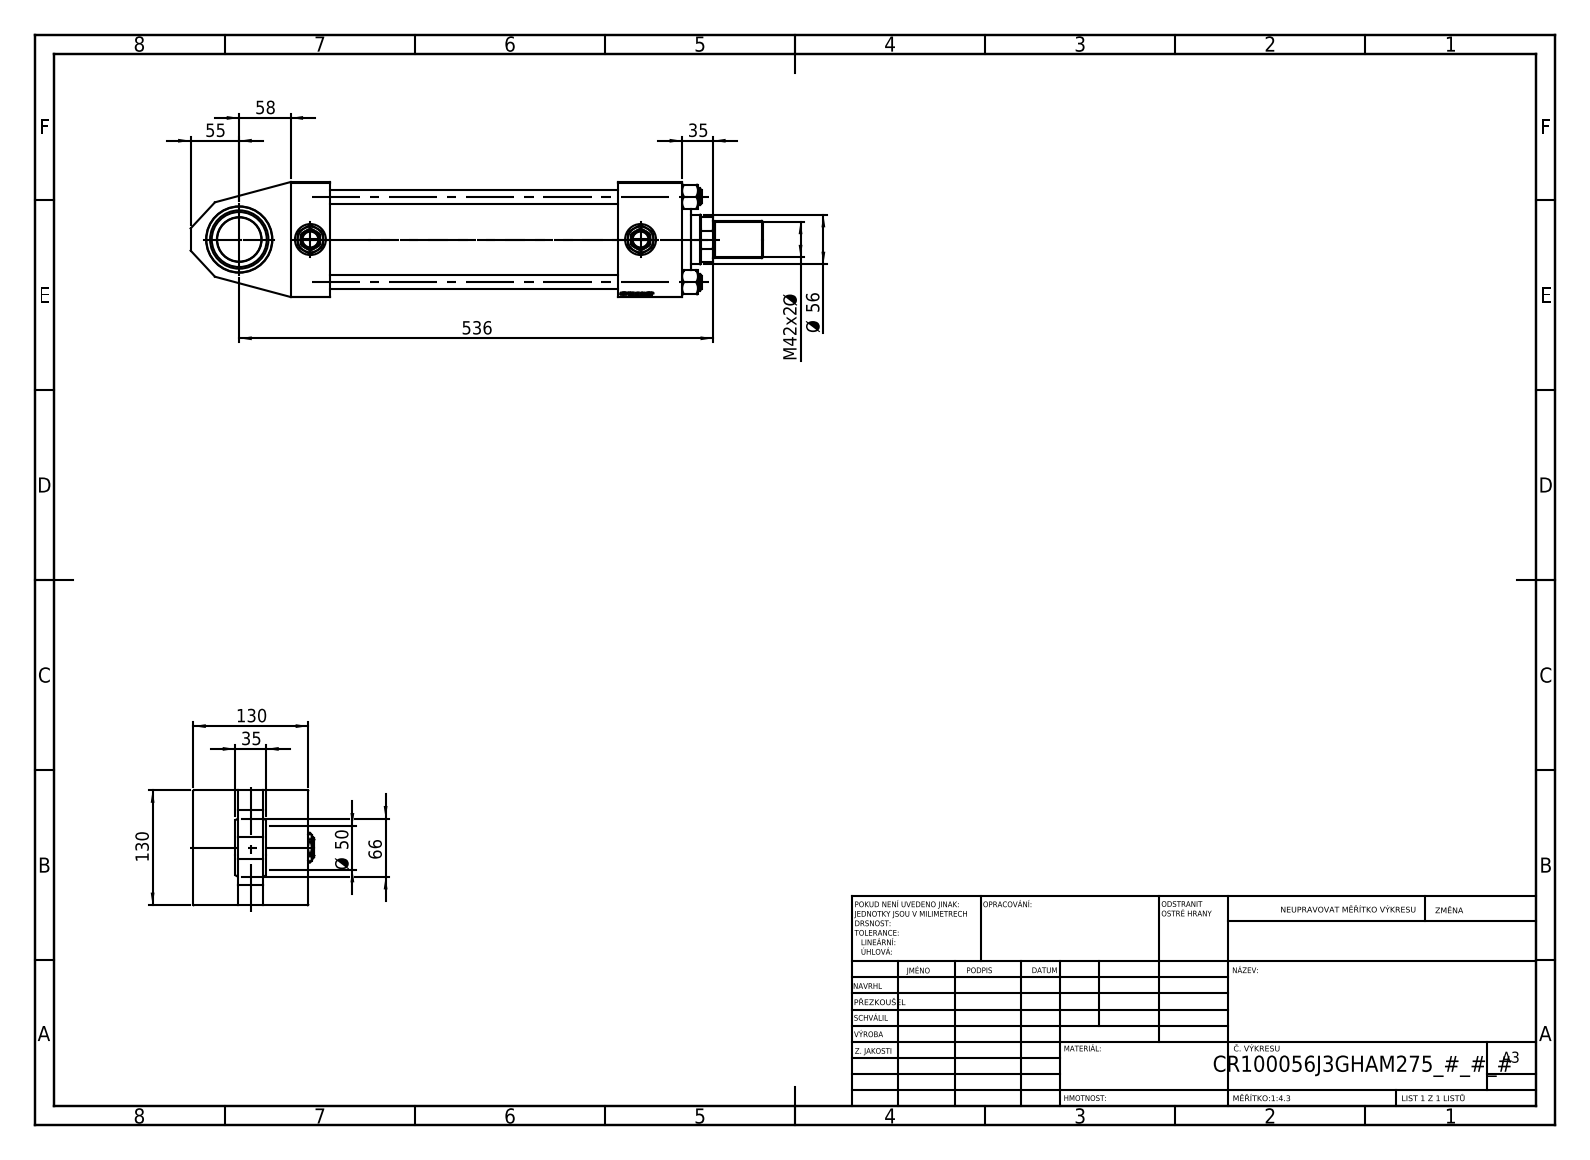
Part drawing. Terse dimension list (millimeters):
name: V215CR_J_VNITRNI_KROUZEK; ROD_END_AH; V215CR_J_Body; NUT_M5_J (+4 more)
written by: SolidWorks 2019 (CONFIG_CONTROL_DESIGN)
unit: mm
bodies: 15 solids, 1308 faces (616 planar, 104 cylindrical, 588 other)
size: 647 × 137 × 130
volume: 3 895 000 mm³; area: 657 826 mm²
holes: 4× ⌀16, 2× ⌀2.5, 2× ⌀7, 2× ⌀26.44, 2× ⌀35, 1× ⌀40.5, 1× ⌀50, 1× ⌀56, 1× ⌀59, 1× ⌀75, 1× ⌀76, 1× ⌀85.5
bosses: 4× ⌀19, 1× ⌀106, 1× ⌀72, 1× ⌀42, 1× ⌀40
rounds: 1× R27
face distances: 130, 51, 79, 45, 443, 398, 371, 326, 72, 28
hole spacings: 49.02, 68.52, 96.9, 101.73, 41, 137.04, 80.5, 82
